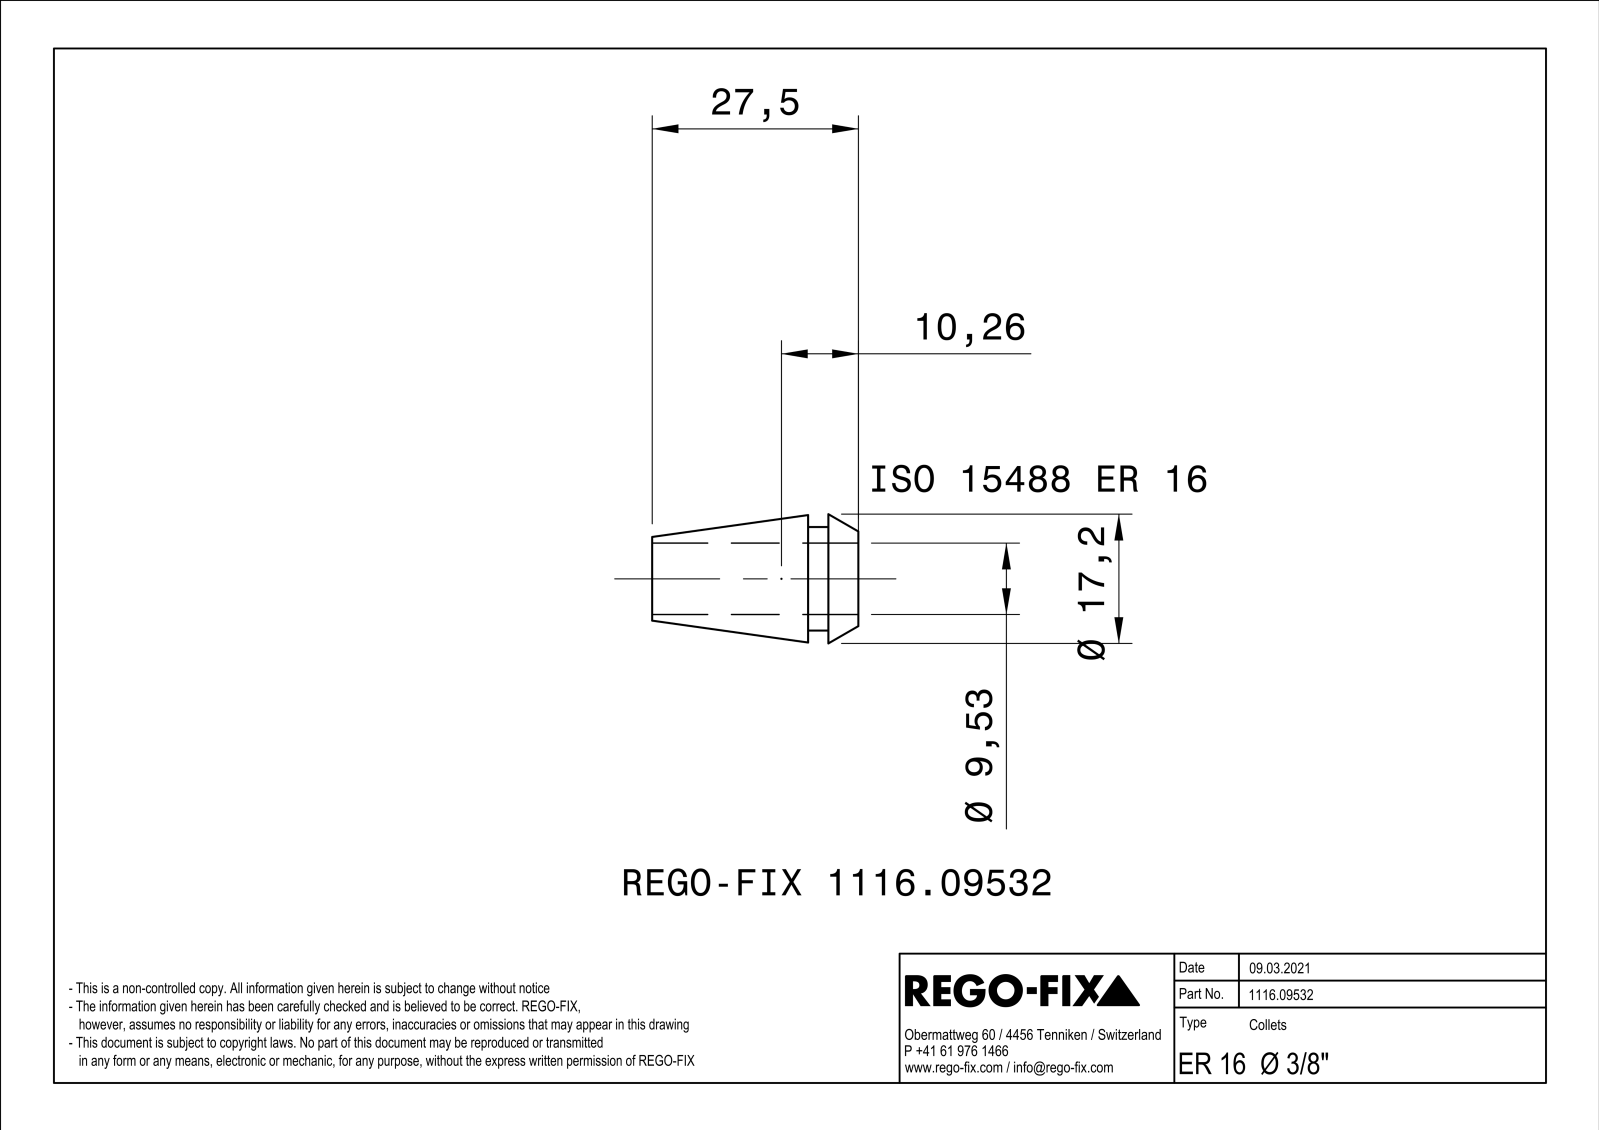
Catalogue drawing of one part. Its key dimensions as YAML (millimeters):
part_name: "NOCUT"
step_written_by: "SIEMENS PLM Software Solid Edge ST10 (AUTOMOTIVE_DESIGN)"
units: millimeters
bodies: {solids: 1, faces: 153, planar: 72, cylindrical: 25, other: 56}
overall_size: [27.5, 17.24, 17.24]
volume: 1889
surface_area: 3645
round_holes:
  - {diameter: 9.53, count: 1}
round_bosses_or_shafts:
  - {diameter: 13.8, count: 1}
partial_cylinders:
  - {radius: 0.3, count: 8}
face_to_face_distances: [0.6, 2.7, 4, 6.7, 27.5, 23.5, 20.8]
